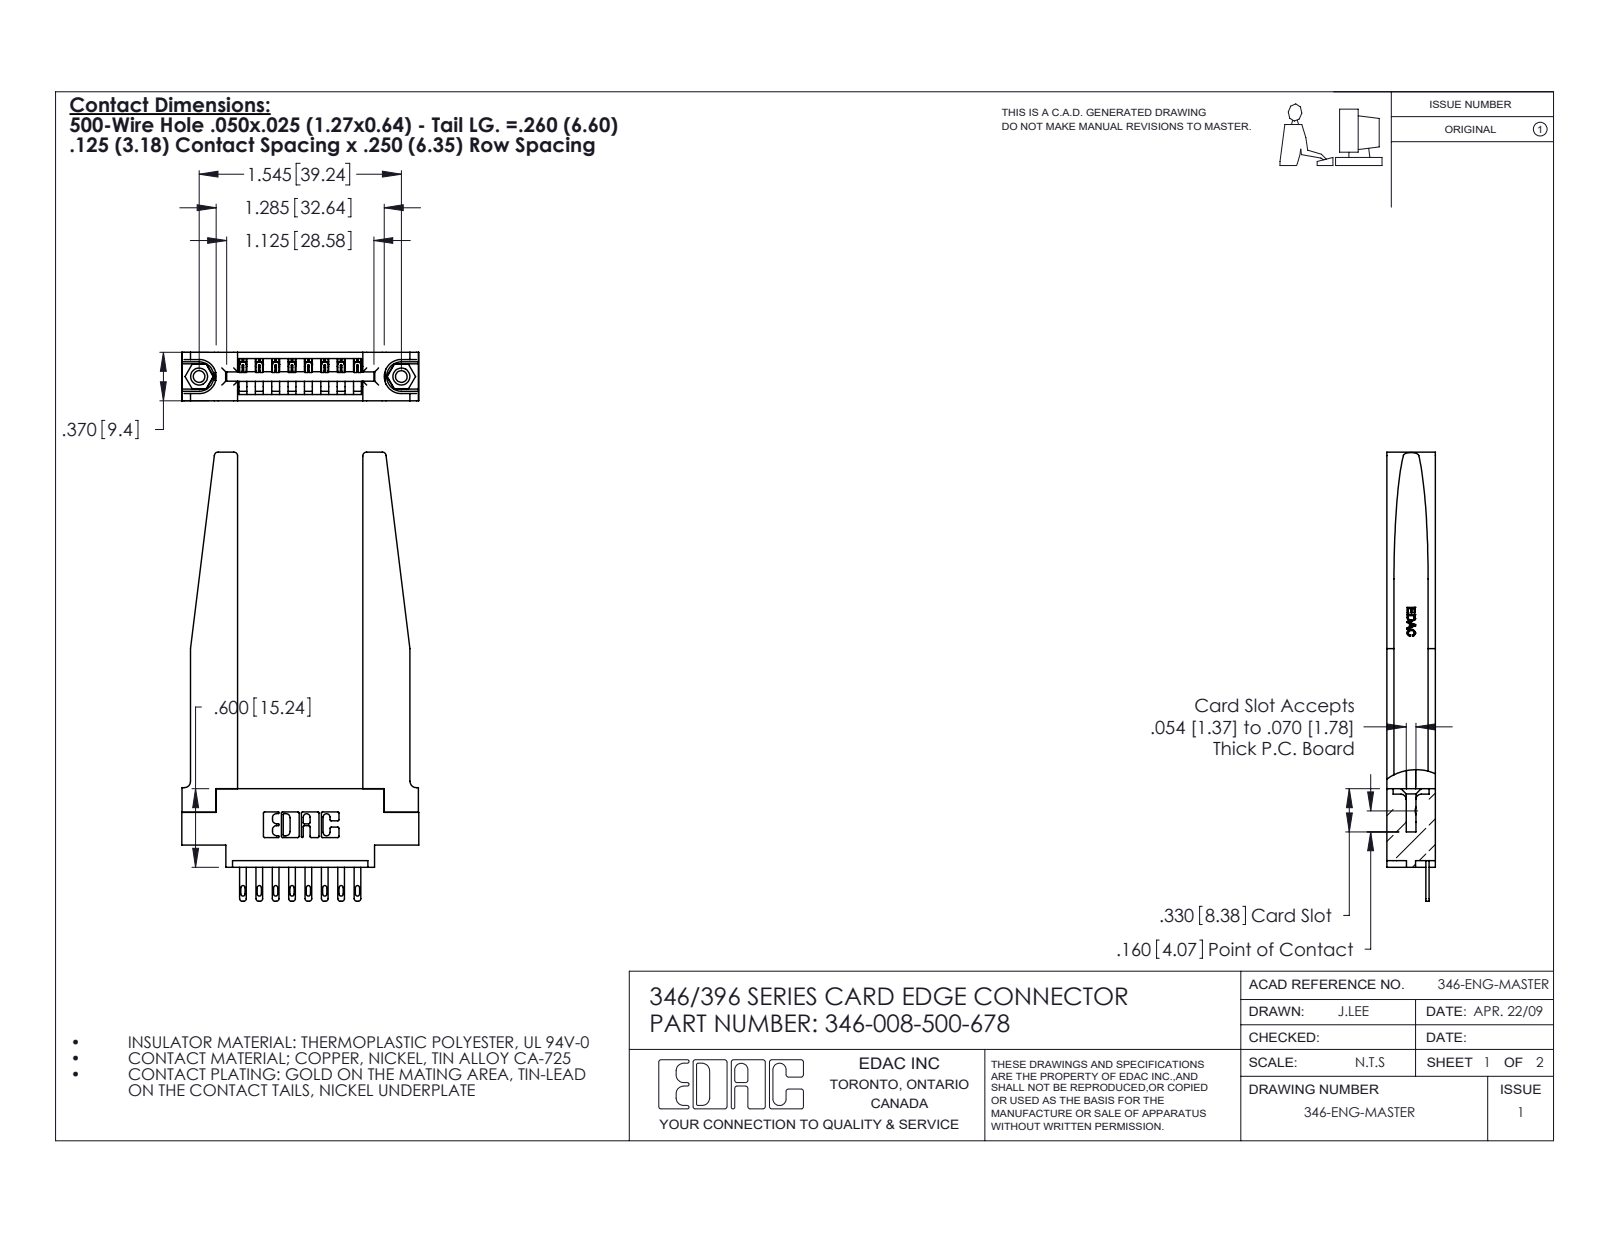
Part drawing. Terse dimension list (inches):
name: 346-220-078_345-220-078; 345-292-001_345-293-100; 346-008-500-678; 345-250-001_345-250-001-102 (+1 more)
written by: SolidWorks 2020 (CONFIG_CONTROL_DESIGN)
unit: in
bodies: 13 solids, 806 faces (508 planar, 246 cylindrical, 52 other)
size: 3.43 × 1.81 × 0.37
volume: 0.666 in³; area: 17.64 in²
holes: 2× ⌀0.089, 2× ⌀0.125, 2× ⌀0.156, 1× ⌀0.064
bosses: 2× ⌀0.155
rounds: 22× R0.01, 16× R0.006, 16× R0.016, 16× R0.02, 8× R0.03, 6× R0.007, 6× R0.031, 3× R0.026
face distances: 0.37, 0.15, 0.22, 0.072, 0.148, 0.25, 0.048, 0.322, 0.956, 0.102
hole spacings: 0.246, 1.341, 1.545
